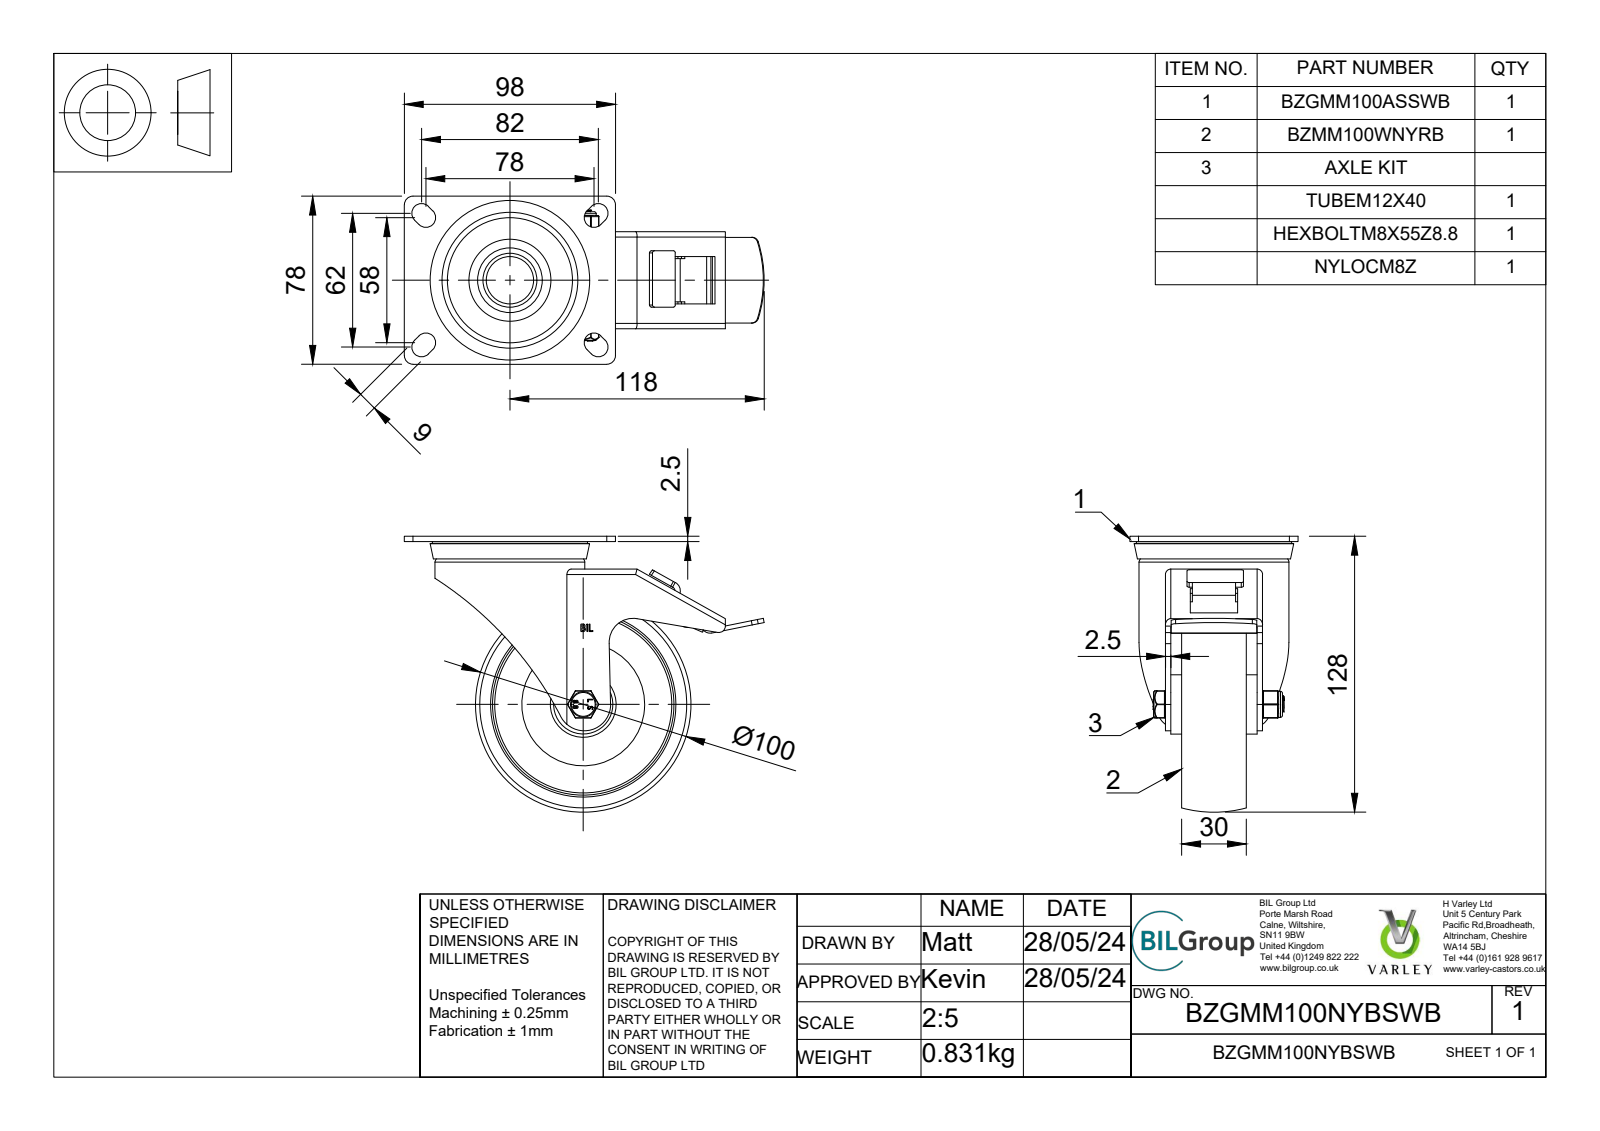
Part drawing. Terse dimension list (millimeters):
name: BZGMM100NYBSWB v3; BZGMM100ASSWB - 2 v1; ZINC PLATED, PRESSED STEEL FORKS; BRAKE PAD (+7 more)
written by: Autodesk Translation Framework v13.14.0.145 (AUTOMOTIVE_DESIGN)
unit: mm
bodies: 48 solids, 579 faces (255 planar, 204 cylindrical, 120 other)
size: 167 × 128 × 78
volume: 216 177 mm³; area: 119 534 mm²
holes: 2× ⌀0.66, 1× ⌀8, 1× ⌀8.2, 1× ⌀8.4, 1× ⌀8.6, 1× ⌀12.2, 1× ⌀12.5, 1× ⌀20, 1× ⌀26, 1× ⌀30, 1× ⌀64.5
bosses: 8× ⌀3.75, 1× ⌀69.5, 1× ⌀47, 1× ⌀27.5, 1× ⌀25, 1× ⌀19.5, 1× ⌀12.1, 1× ⌀11.9
rounds: 18× R0.5, 12× R0.25, 8× R1.25, 8× R4.5, 5× R4, 4× R0.33, 4× R0.64, 4× R1
face distances: 2.5, 7.5, 18.75, 16.25, 23.75, 26.25, 42.5, 5, 11.25, 3
hole spacings: 3.22, 2.49
